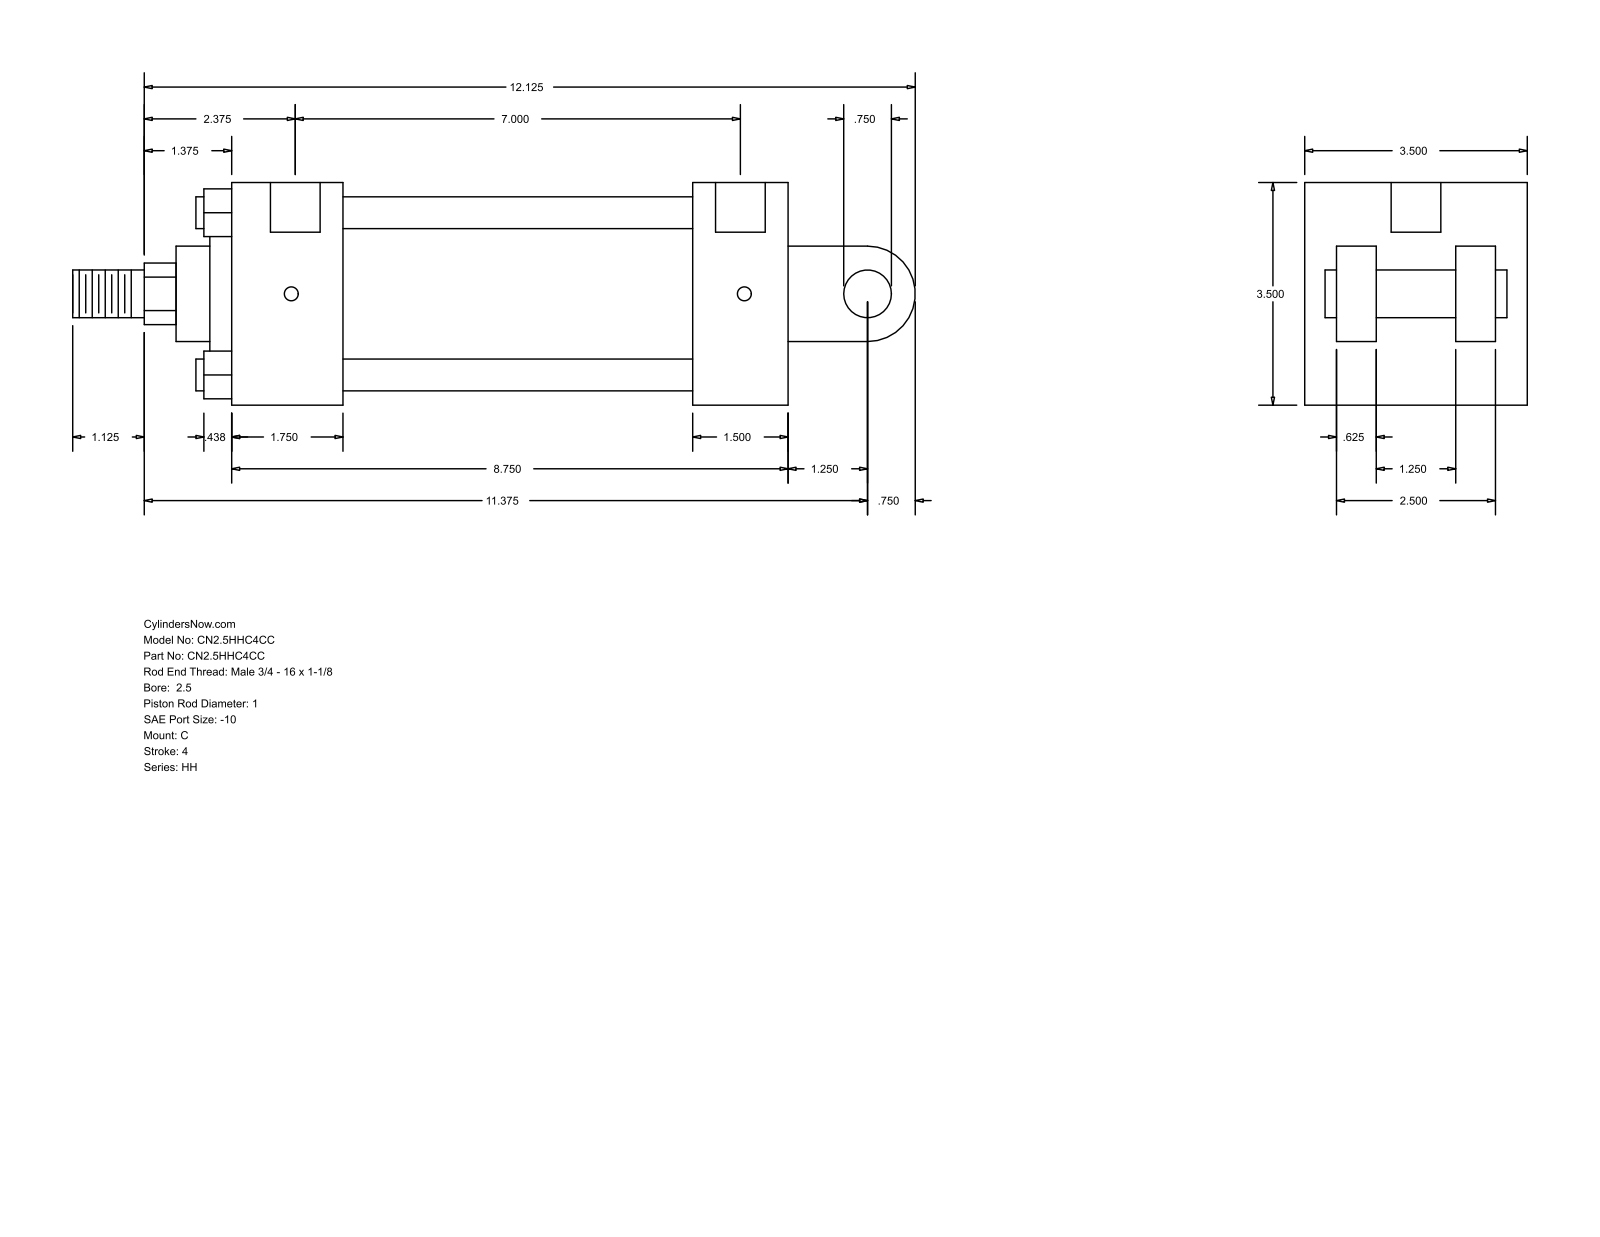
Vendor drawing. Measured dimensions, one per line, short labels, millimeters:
name: HH_C__0250_1
written by: GSSL Pune (CONFIG_CONTROL_DESIGN)
unit: mm
bodies: 0 solids, 101 faces (71 planar, 30 cylindrical, 0 other)
size: 336.55 × 88.9 × 88.9
holes: 4× ⌀5.56, 2× ⌀19.84
bosses: 4× ⌀12.7, 2× ⌀19.05, 1× ⌀73.03, 1× ⌀60.33, 1× ⌀38.1, 1× ⌀25.4
rounds: 1× R12.29, 1× R19.05
face distances: 88.9, 222.26, 63.5, 184.15, 38.11, 44.46, 139.69, 177.8, 12.7, 28.57
hole spacings: 1.59, 179.38, 180.97, 177.79
